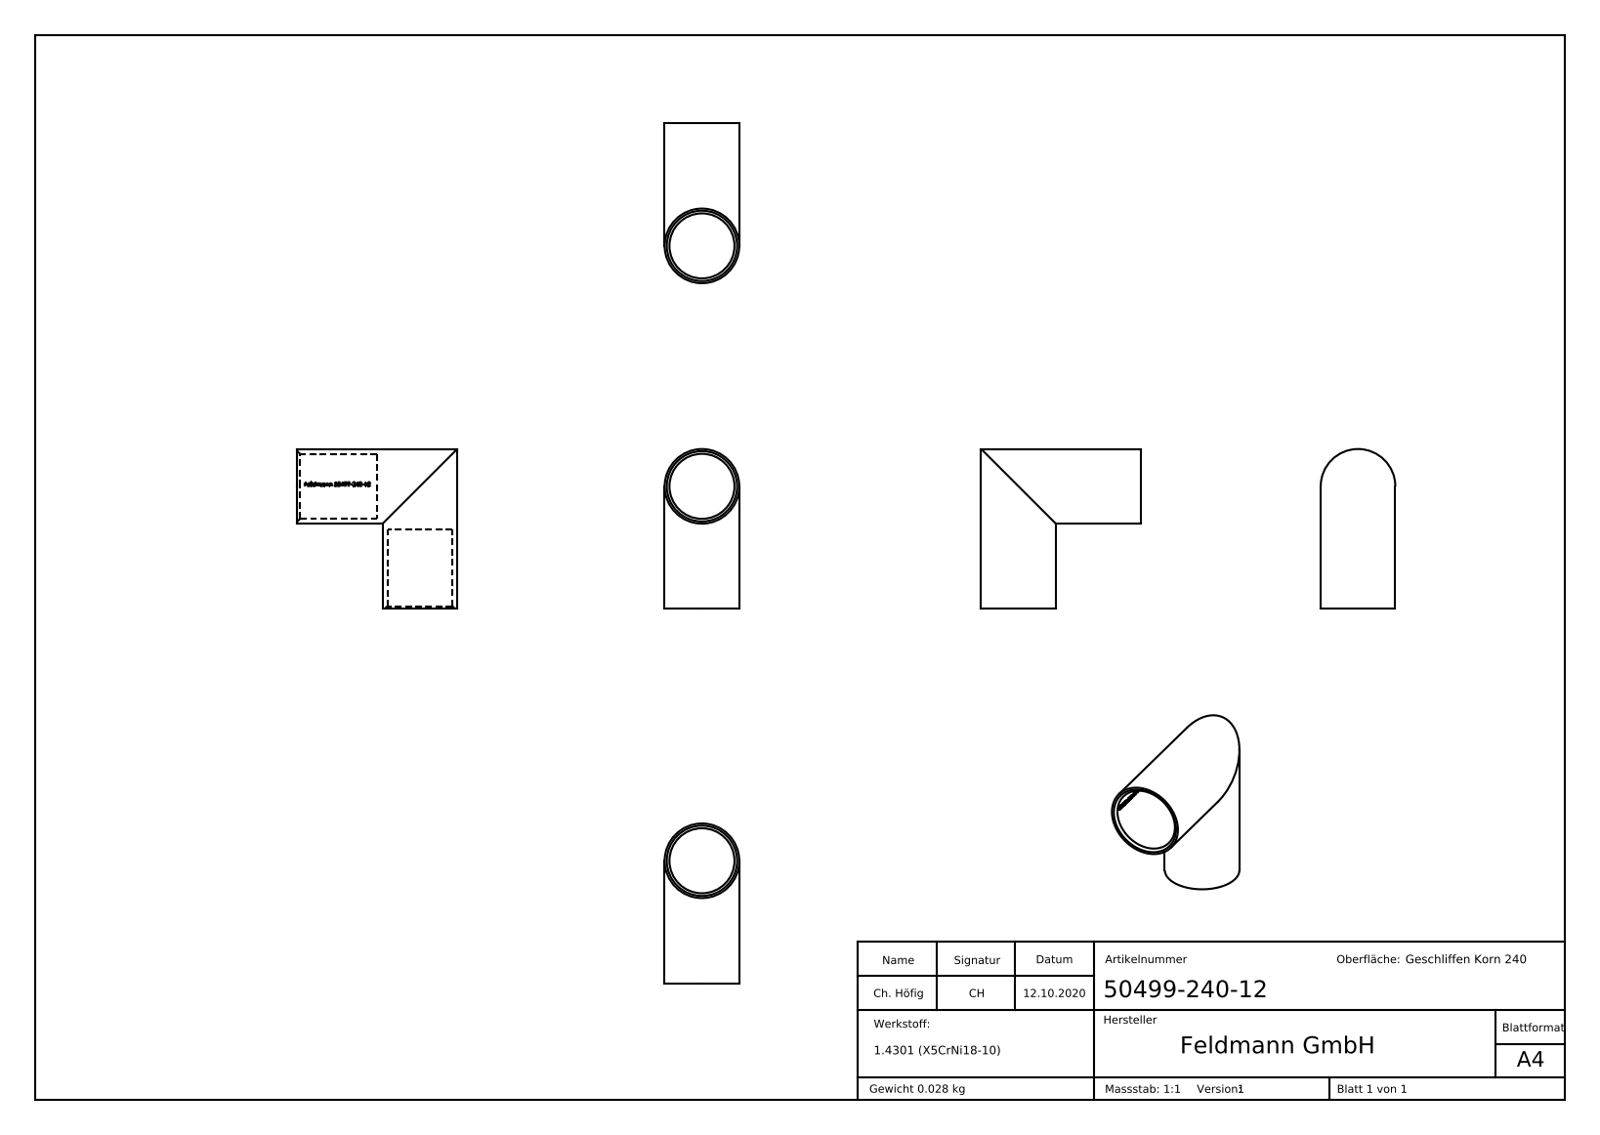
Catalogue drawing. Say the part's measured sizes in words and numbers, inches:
The part is named "50499-240-12". Its 3-D file was written by "SolidWorks 2018 (CONFIG_CONTROL_DESIGN)". It is 1 solid with 269 faces: 129 planar, 38 cylindrical and 102 other. Overall it measures 1.181 by 1.181 by 0.551 inches. Its volume is 0.217 cubic inches and its surface area 5.372 square inches. Round holes: 2 of diameter 0.48. Round bosses or shafts: 2 of diameter 0.551. Partial cylindrical surfaces (rounded edges, fillets, slot ends): 1 of radius 0.244. The main face-to-face distances are 0.591, 0.087, 0.393, 0.866, 0.276, 0.876, 0.286, 0.021, 0.403, 0.048.
